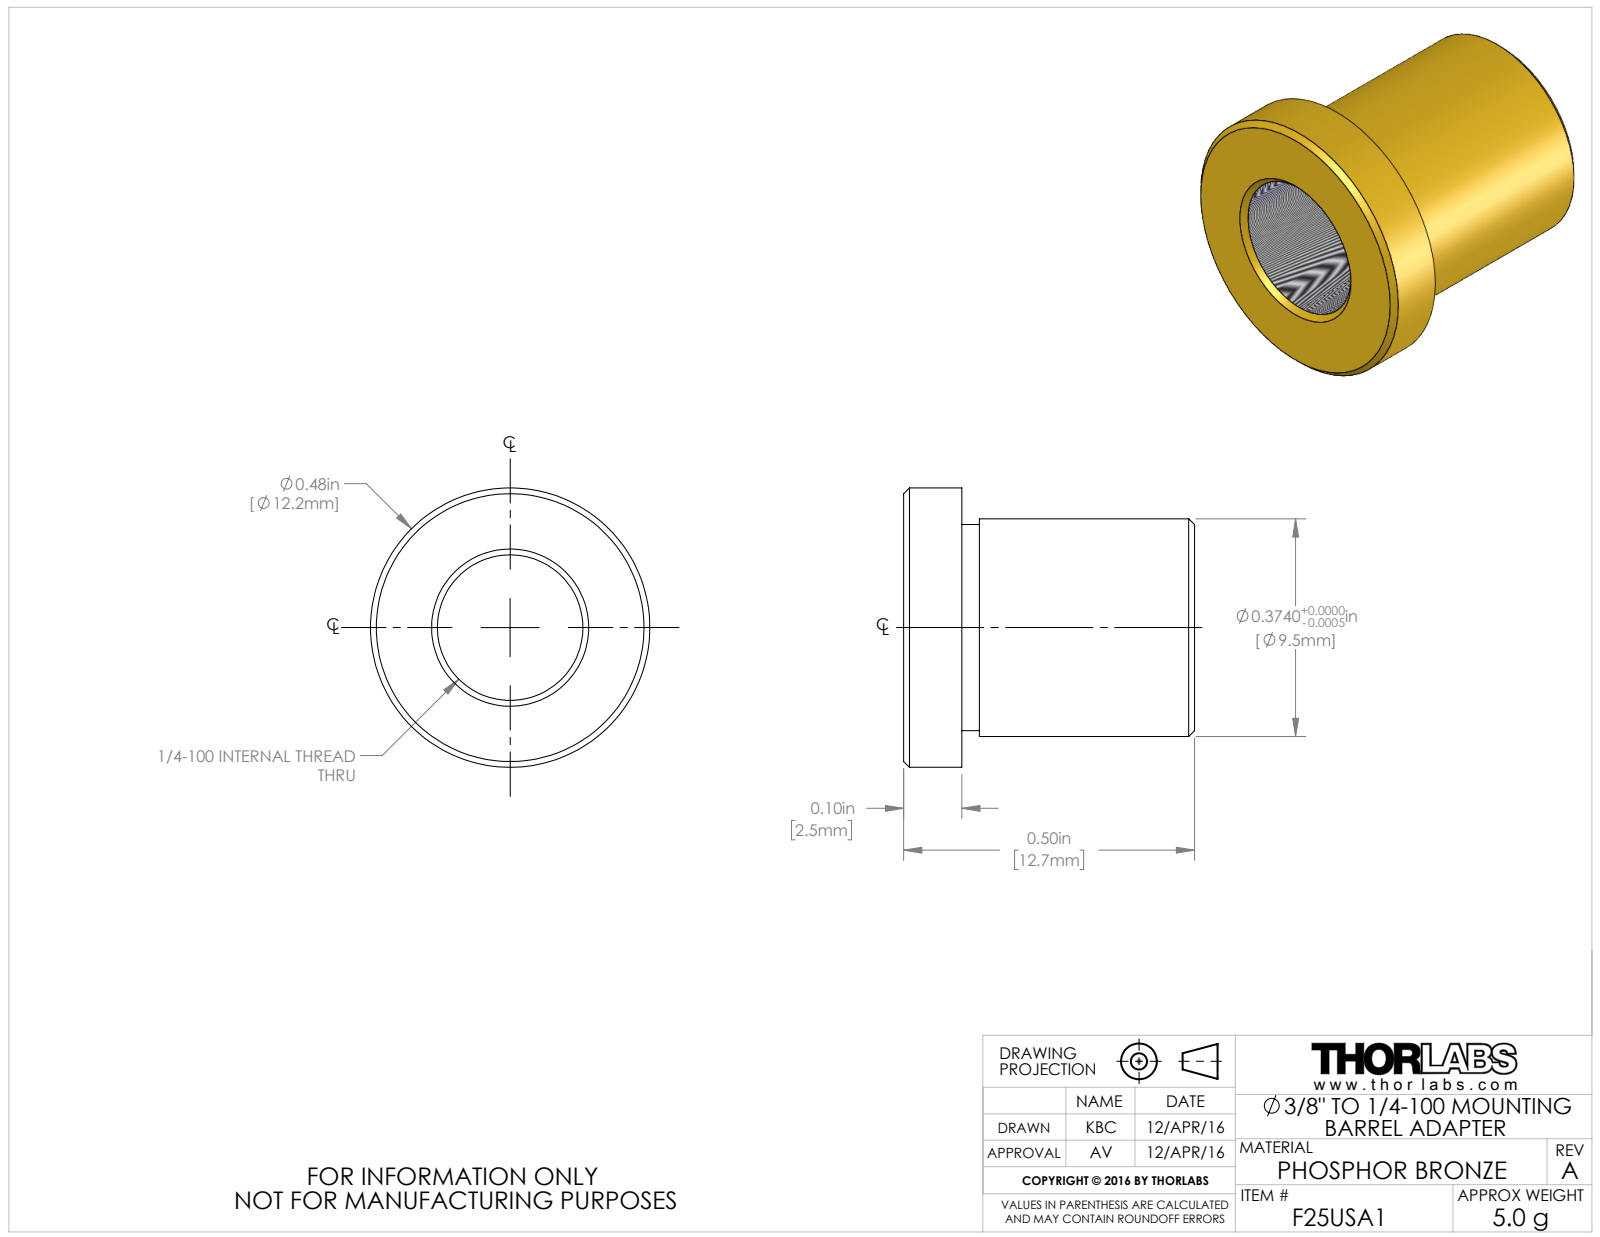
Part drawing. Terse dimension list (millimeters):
name: TTN099739-E0W
written by: SolidWorks 2014 (CONFIG_CONTROL_DESIGN)
unit: mm
bodies: 1 solid, 20 faces (4 planar, 8 cylindrical, 8 other)
size: 12.7 × 12.2 × 12.2
volume: 610 mm³; area: 821 mm²
holes: 1× ⌀6.4
bosses: 1× ⌀12.2, 1× ⌀9.5, 1× ⌀9
face distances: 2.5, 10.2, 12.7, 9.4, 0.8, 3.3
